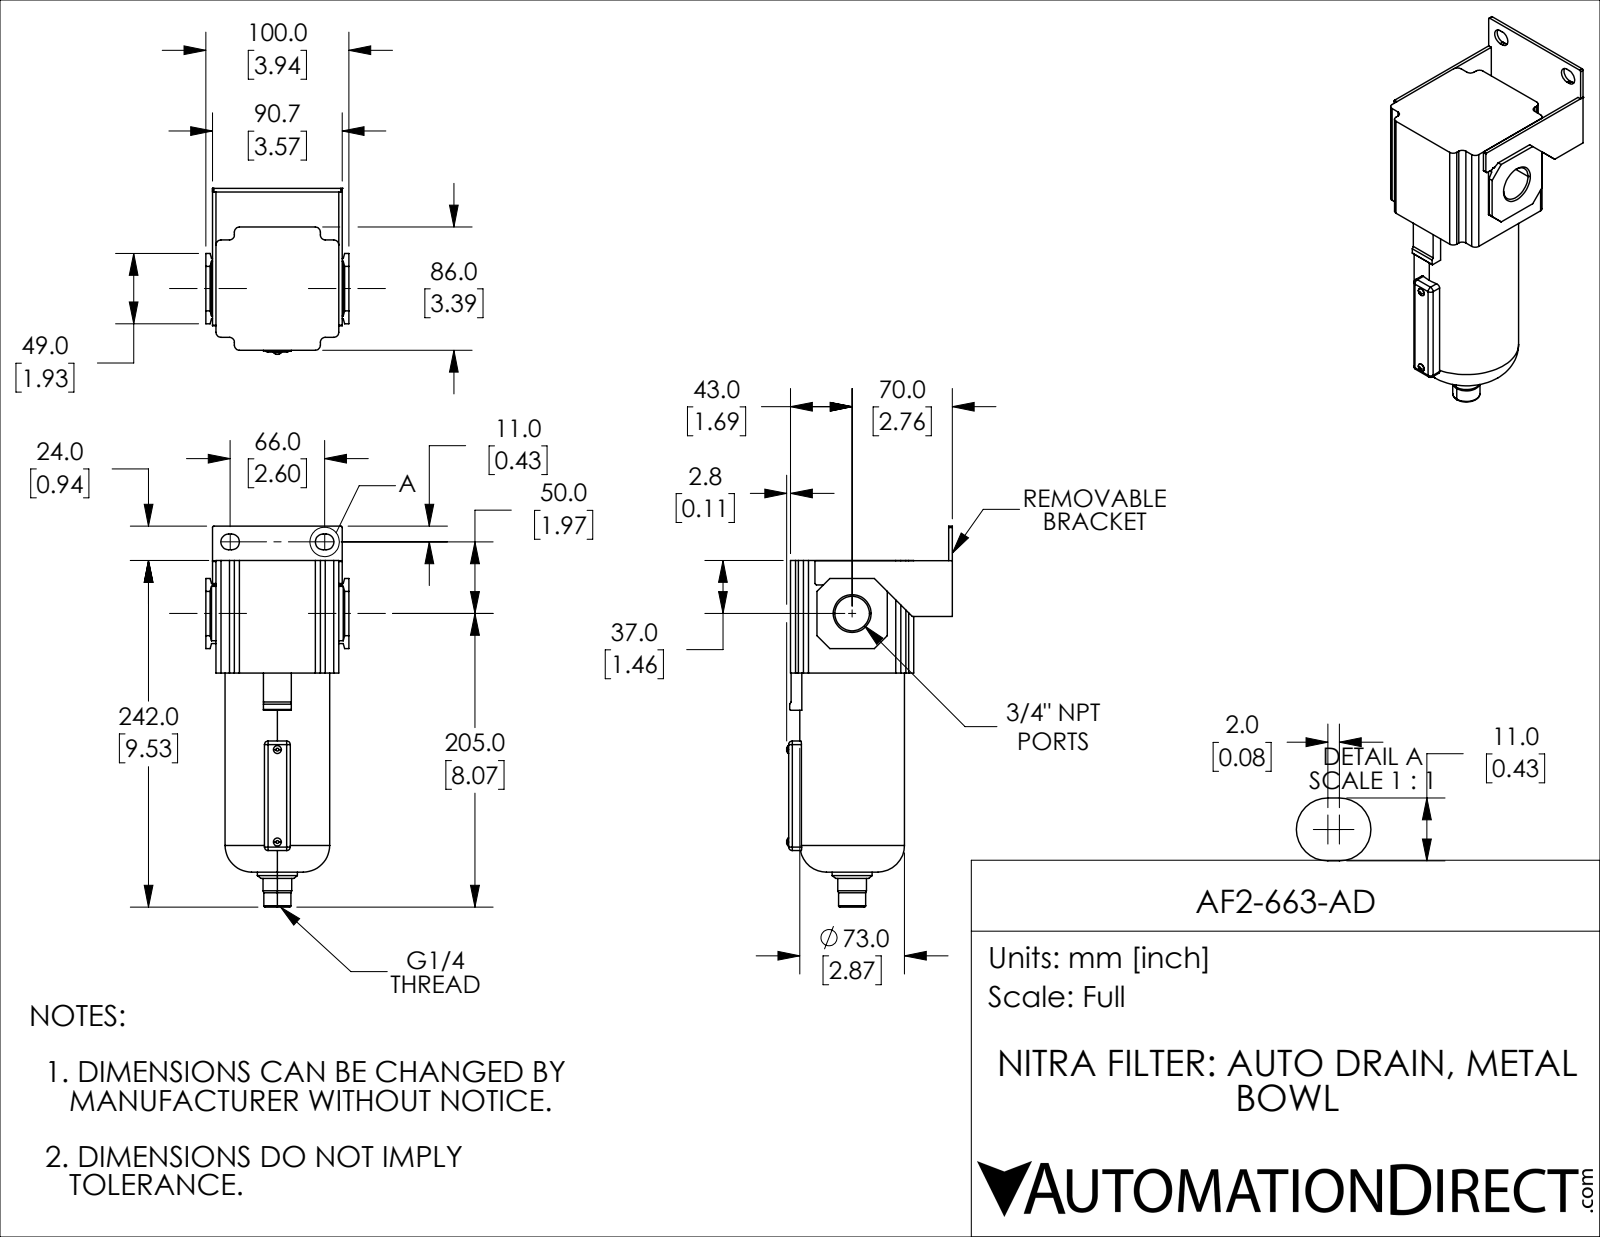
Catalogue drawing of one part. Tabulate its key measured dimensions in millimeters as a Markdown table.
| quantity | value |
| --- | --- |
| part name | AF2-663-AD |
| STEP written by | SolidWorks 2019 (CONFIG_CONTROL_DESIGN) |
| units | millimeters |
| bodies | 1 solid, 160 faces (94 planar, 44 cylindrical, 22 other) |
| overall size | 266 × 115.8 × 100 |
| volume | 1 160 000 mm³ |
| surface area | 98 586 mm² |
| round holes (diameter × count) | 8.57 × 1, 24.12 × 1 |
| round bosses / shafts (diameter × count) | 5.5 × 2, 73 × 1, 28 × 1, 20 × 1, 19 × 1 |
| partial cylindrical surfaces (radius × count) | 3.5 × 12, 2.5 × 8, 5.5 × 4, 1 × 2 |
| main face-to-face distances | 2.5, 88.2, 24.5, 113, 86, 27, 110.5, 85.7, 4.65, 7.15 |
